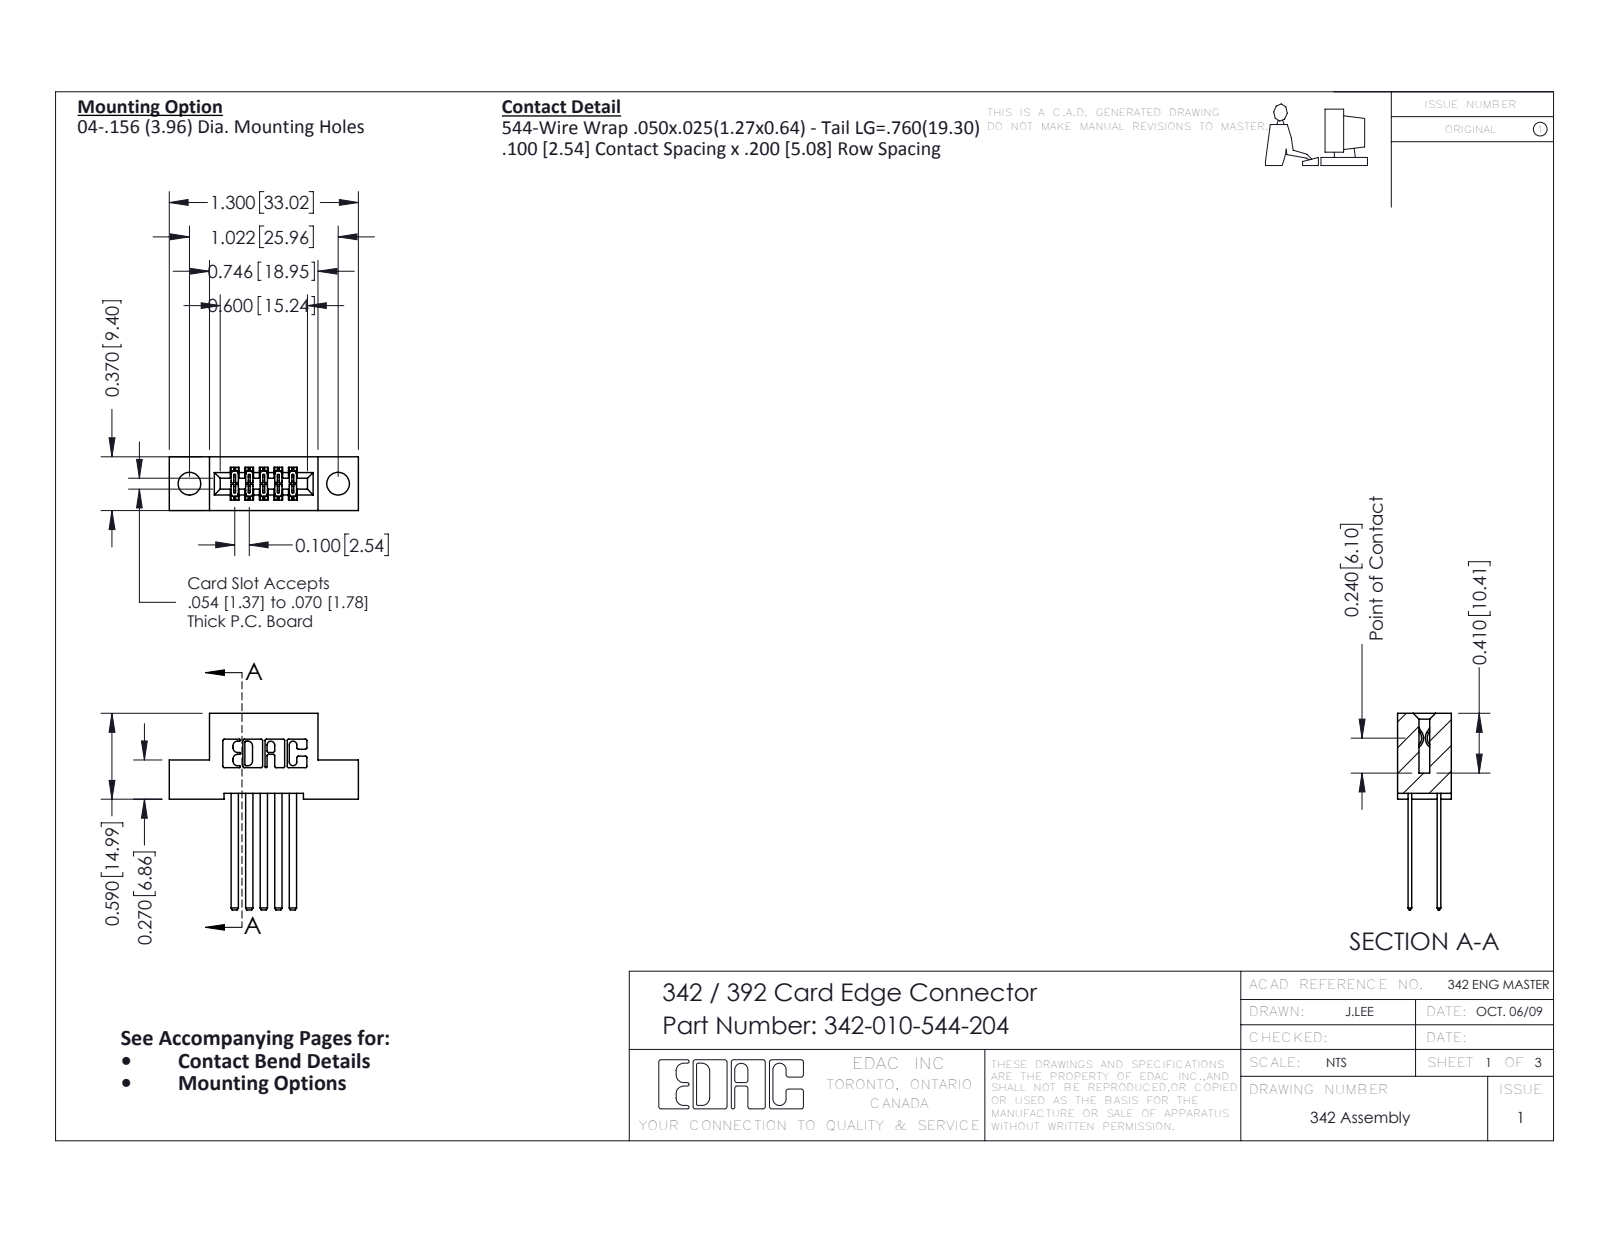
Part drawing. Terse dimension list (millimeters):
name: 342 Part_.156 TH; 345-292-001_345-293-144; 342-010-544-204
written by: SolidWorks 2016 (CONFIG_CONTROL_DESIGN)
unit: mm
bodies: 11 solids, 570 faces (386 planar, 184 cylindrical, 0 other)
size: 34.3 × 33 × 9.4
volume: 2 850 mm³; area: 3 932 mm²
holes: 2× ⌀4
rounds: 22× R0.3, 15× R0.2, 6× R0.2, 6× R0.8, 3× R0.7, 2× R0.4, 2× R0.6, 2× R0.6
face distances: 5.1, 1.8, 7.6, 2.5, 2.5, 6.9, 0.6, 9.4, 1, 5.7
hole spacings: 26
